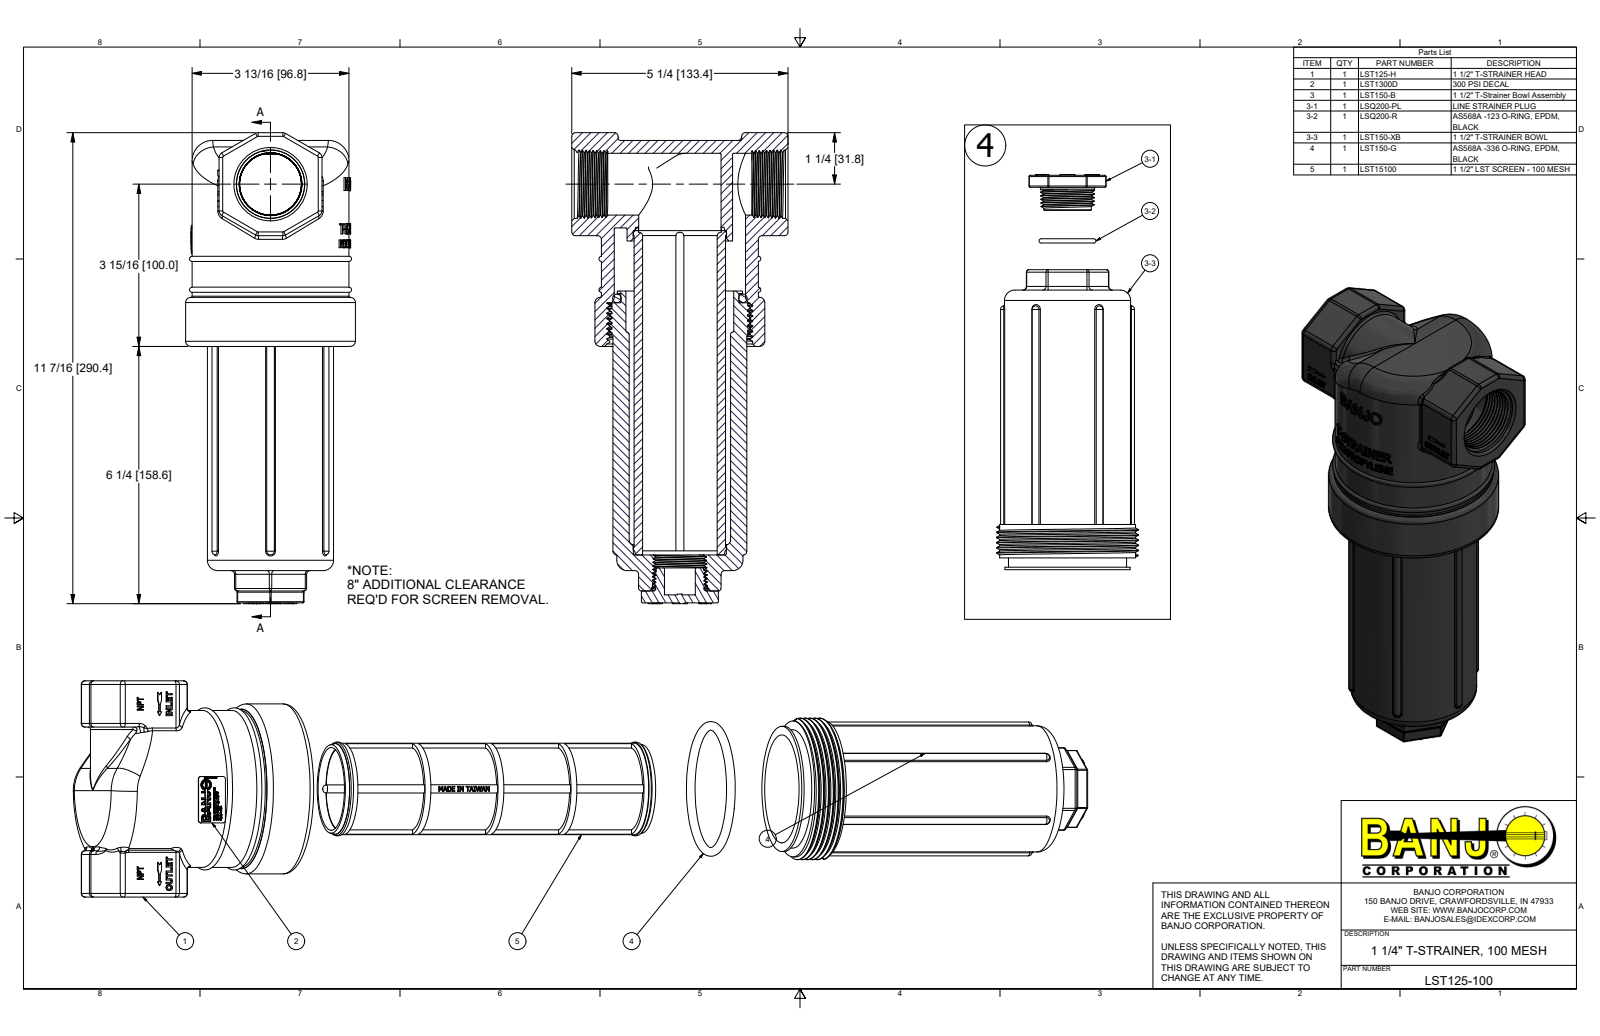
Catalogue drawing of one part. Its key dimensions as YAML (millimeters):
part_name: "LST125-100; CE050D; LST1300D; LST125-H (+6 more)"
step_written_by: "Autodesk Inventor 2018 (AUTOMOTIVE_DESIGN)"
units: millimeters
bodies: {solids: 8, faces: 3134, planar: 1698, cylindrical: 298, other: 1138}
overall_size: [1226.5, 290.4, 104.8]
volume: 823900
surface_area: 485700
round_holes:
  - {diameter: 4.6, count: 1}
  - {diameter: 6.5, count: 1}
  - {diameter: 19.1, count: 1}
  - {diameter: 38.1, count: 1}
  - {diameter: 46, count: 1}
  - {diameter: 50, count: 1}
  - {diameter: 50.8, count: 1}
  - {diameter: 57.4, count: 1}
  - {diameter: 57.5, count: 1}
  - {diameter: 66.5, count: 1}
  - {diameter: 81, count: 1}
  - {diameter: 86.4, count: 1}
round_bosses_or_shafts:
  - {diameter: 104.8, count: 1}
  - {diameter: 96.8, count: 1}
  - {diameter: 87.2, count: 1}
  - {diameter: 83.8, count: 1}
  - {diameter: 77.8, count: 1}
  - {diameter: 77.2, count: 1}
  - {diameter: 72.9, count: 1}
  - {diameter: 65.1, count: 1}
partial_cylinders:
  - {radius: 0.8, count: 44}
  - {radius: 2.3, count: 34}
  - {radius: 1.5, count: 16}
  - {radius: 3.2, count: 10}
  - {radius: 2, count: 6}
  - {radius: 2.4, count: 6}
  - {radius: 2.5, count: 4}
  - {radius: 0.7, count: 2}
face_to_face_distances: [63.5, 255.5, 155.4, 100.1, 23.4, 31.5, 247.6, 92.2, 8, 133.4]
